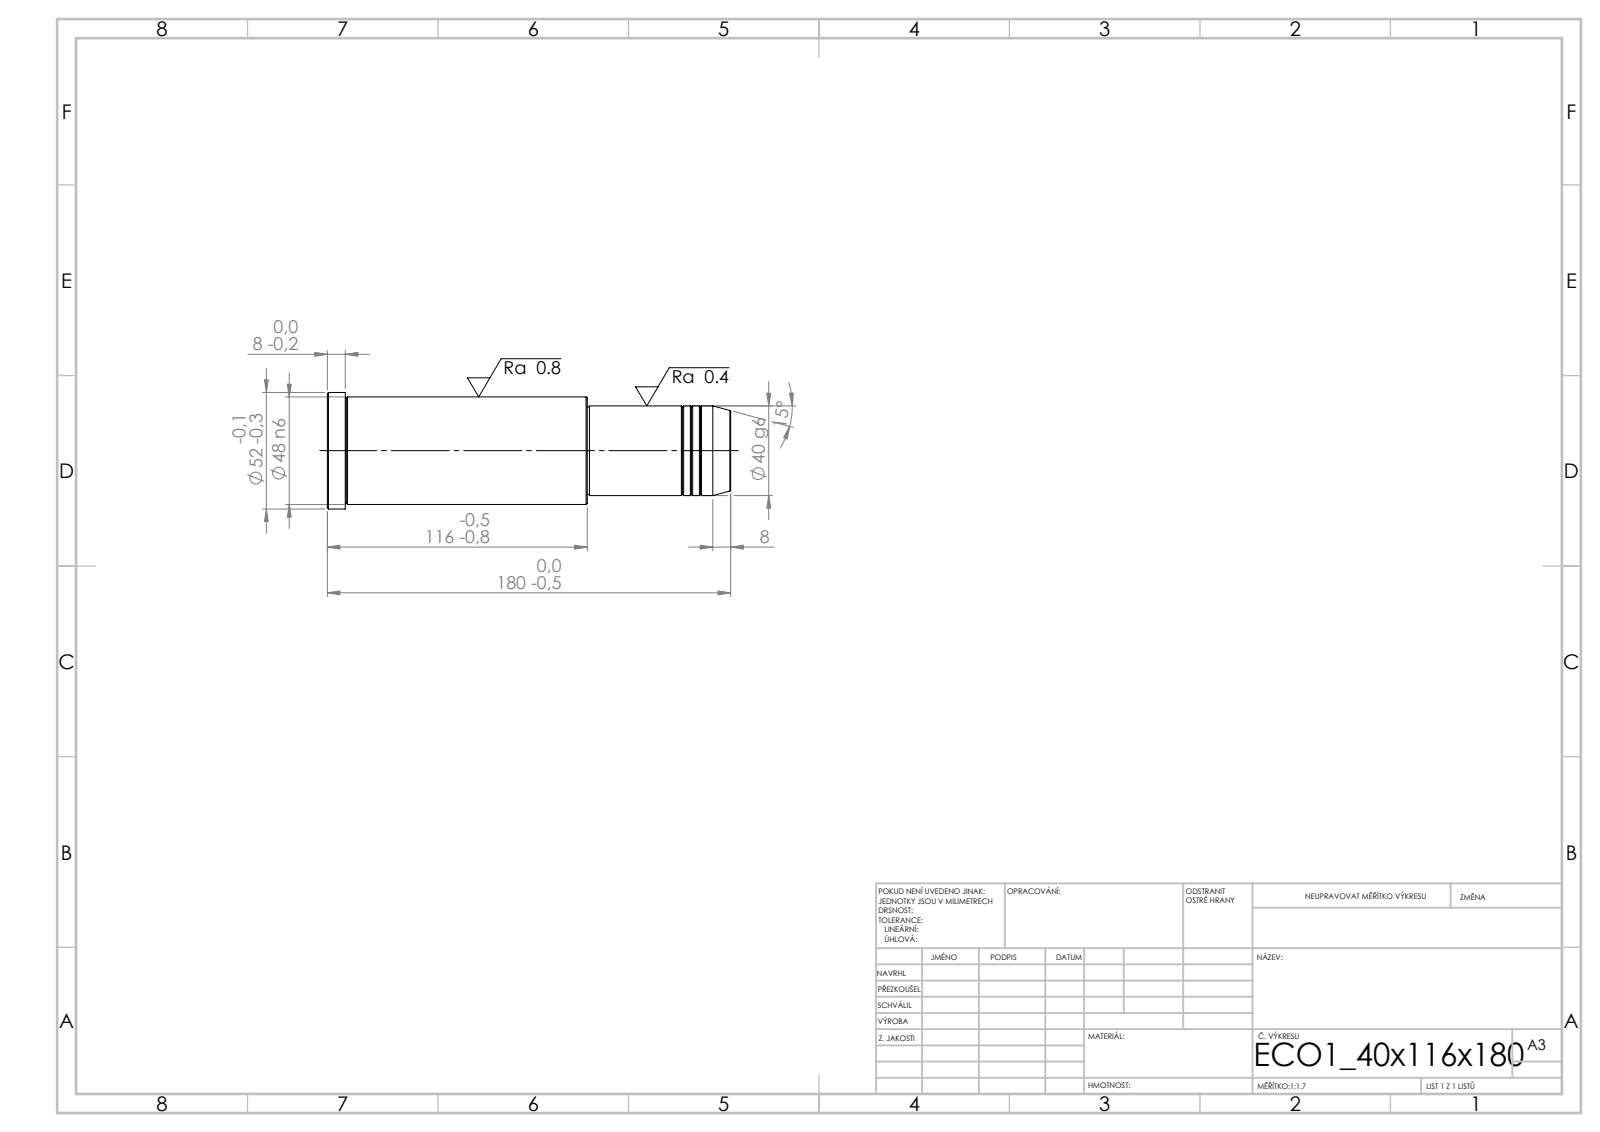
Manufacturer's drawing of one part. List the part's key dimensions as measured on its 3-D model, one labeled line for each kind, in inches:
STEP written by: SolidWorks 2019 (CONFIG_CONTROL_DESIGN)
Units: inches
Bodies: 1 solid, 43 faces (5 planar, 14 cylindrical, 24 other)
Overall size (bounding box): 7.087 × 2.047 × 2.047
Volume: 17.79 in³ · Surface area: 46.36 in²
Round bosses / shafts (diameter × count): ⌀2.047 ×1, ⌀1.89 ×1, ⌀1.575 ×1, ⌀1.535 ×1
Main face-to-face distances: 7.087, 2.52, 4.567, 6.772, 4.252, 0.315, 2.48, 0.039, 4.291, 4.606
